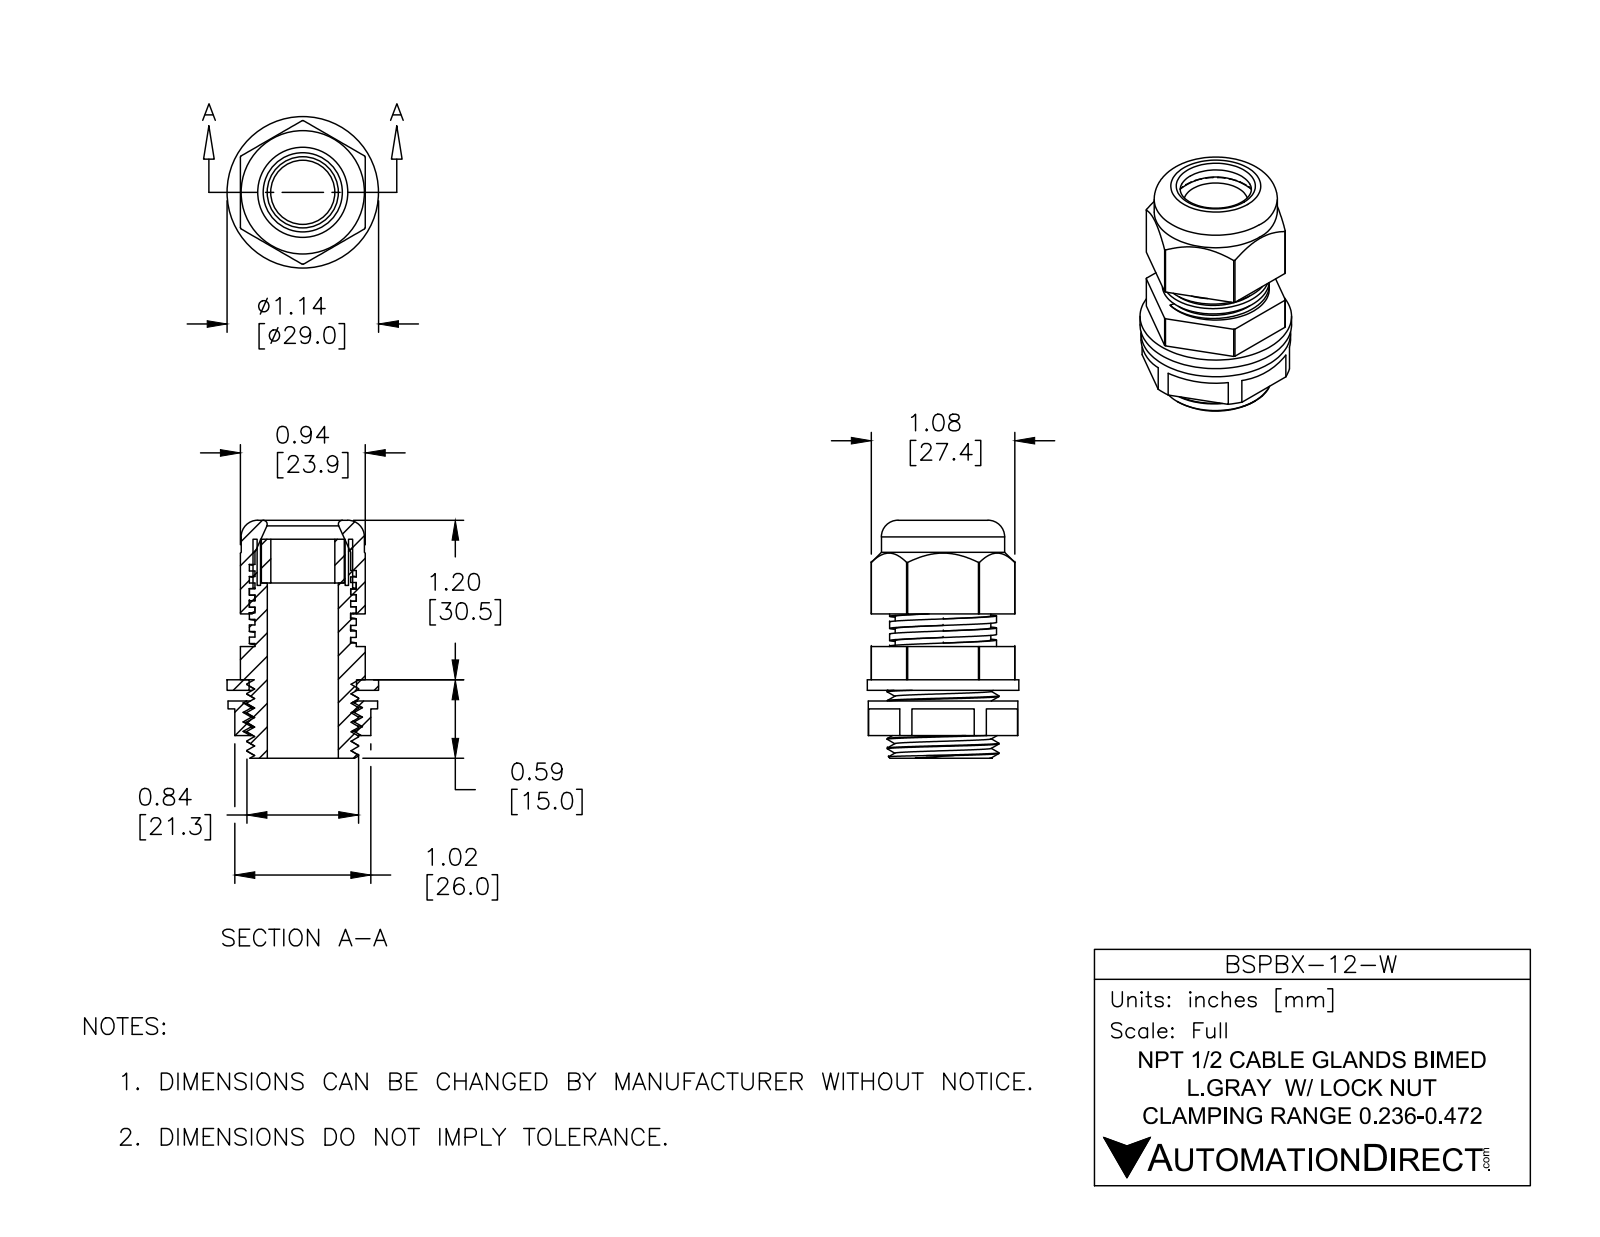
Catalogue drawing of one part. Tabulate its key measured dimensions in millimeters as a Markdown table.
| quantity | value |
| --- | --- |
| part name | BSPBX-12-W |
| STEP written by | SolidWorks 2015 (CONFIG_CONTROL_DESIGN) |
| units | millimeters |
| bodies | 5 solids, 274 faces (129 planar, 119 cylindrical, 26 other) |
| overall size | 45.5 × 29 × 29 |
| volume | 13 700 mm³ |
| surface area | 14 650 mm² |
| round holes (diameter × count) | 12.2 × 1, 13.6 × 1, 18.3 × 1, 19.9 × 1, 20.5 × 1 |
| round bosses / shafts (diameter × count) | 29 × 1, 28.6 × 1, 23.5 × 1, 21.3 × 1, 20.4 × 1, 19.1 × 1, 15.8 × 1 |
| partial cylindrical surfaces (radius × count) | 13.7 × 1 |
| main face-to-face distances | 23.9, 0.5, 1, 24.9, 13.2, 2, 2, 4, 13.7, 6.6 |
